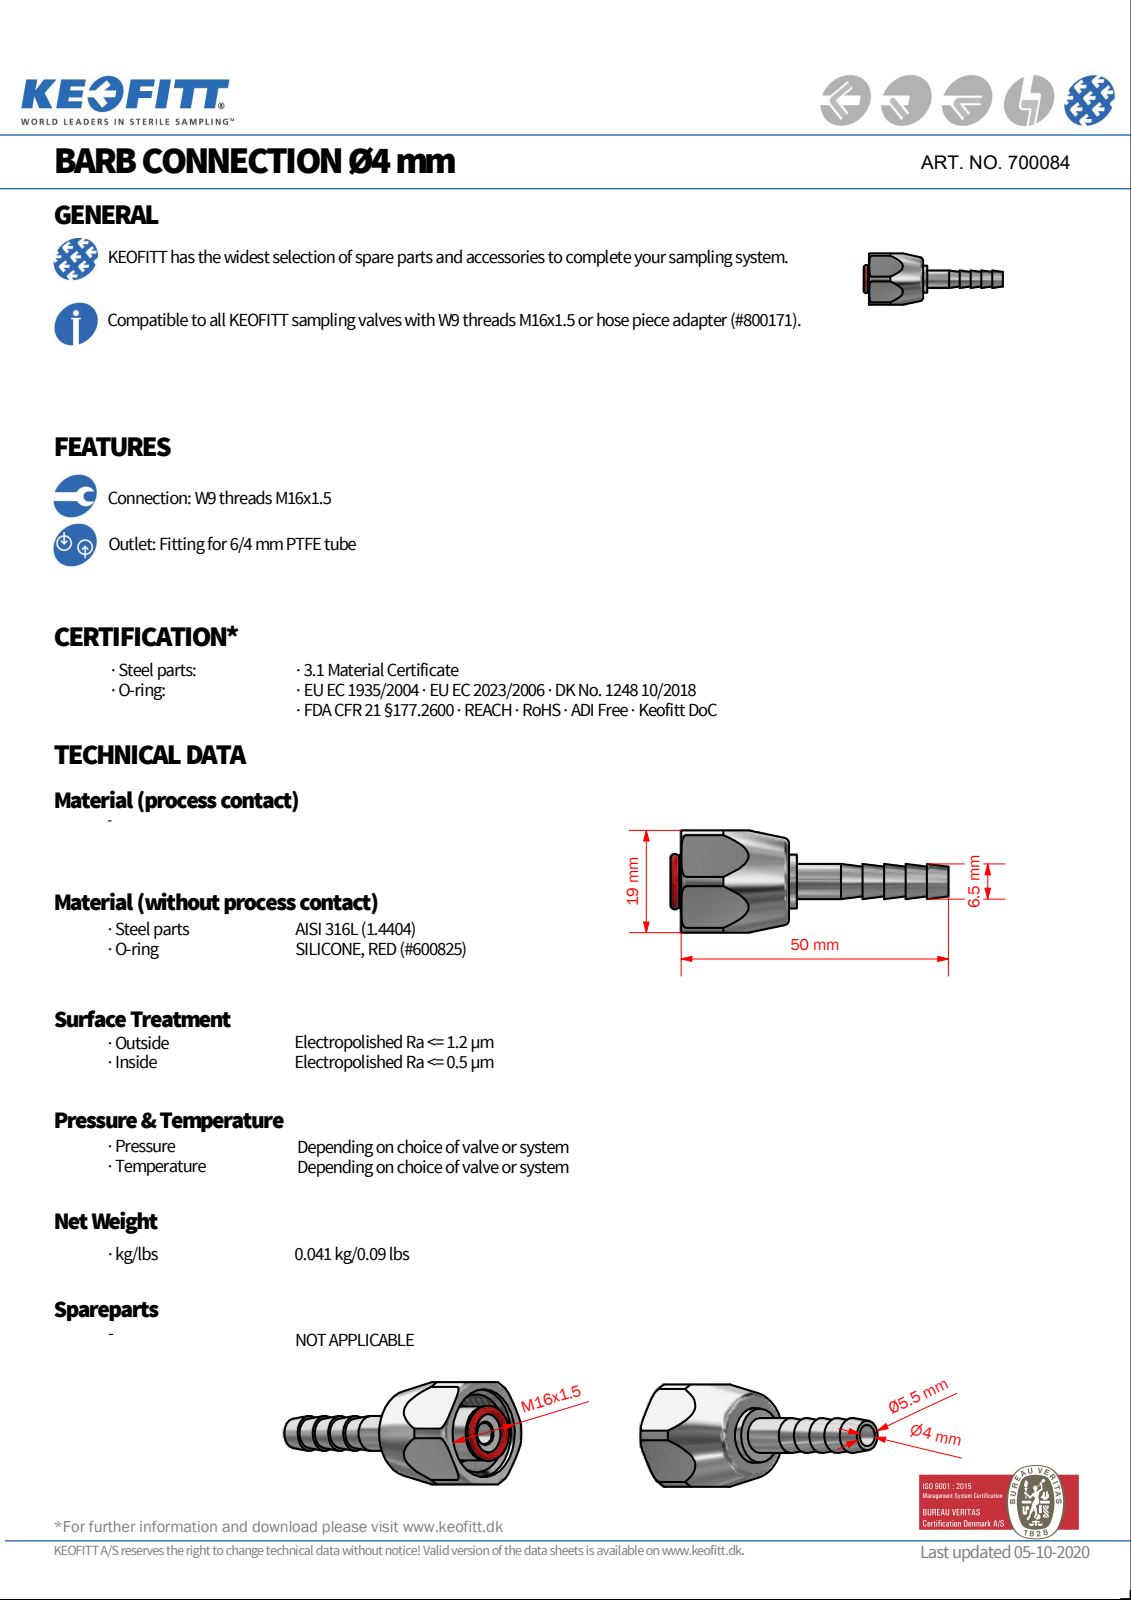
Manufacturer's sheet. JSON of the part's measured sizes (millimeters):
{"part_name": "700084", "step_written_by": "Autodesk Inventor 2022 (AUTOMOTIVE_DESIGN)", "units": "millimeters", "bodies": {"solids": 3, "faces": 49, "planar": 15, "cylindrical": 14, "other": 20}, "overall_size": [51.6, 21, 19], "volume_mm3": 5131, "surface_area_mm2": 4511, "round_holes": [[4, 1], [10.2, 1], [14.5, 1], [16.3, 1]], "round_bosses_or_shafts": [[13, 1], [10, 1], [6.5, 1]], "partial_cylinders_radius": [[10.5, 1]], "face_to_face_distances": [19, 20, 20.37, 0.37, 1.5, 21.5, 21.87, 4, 8, 12]}
